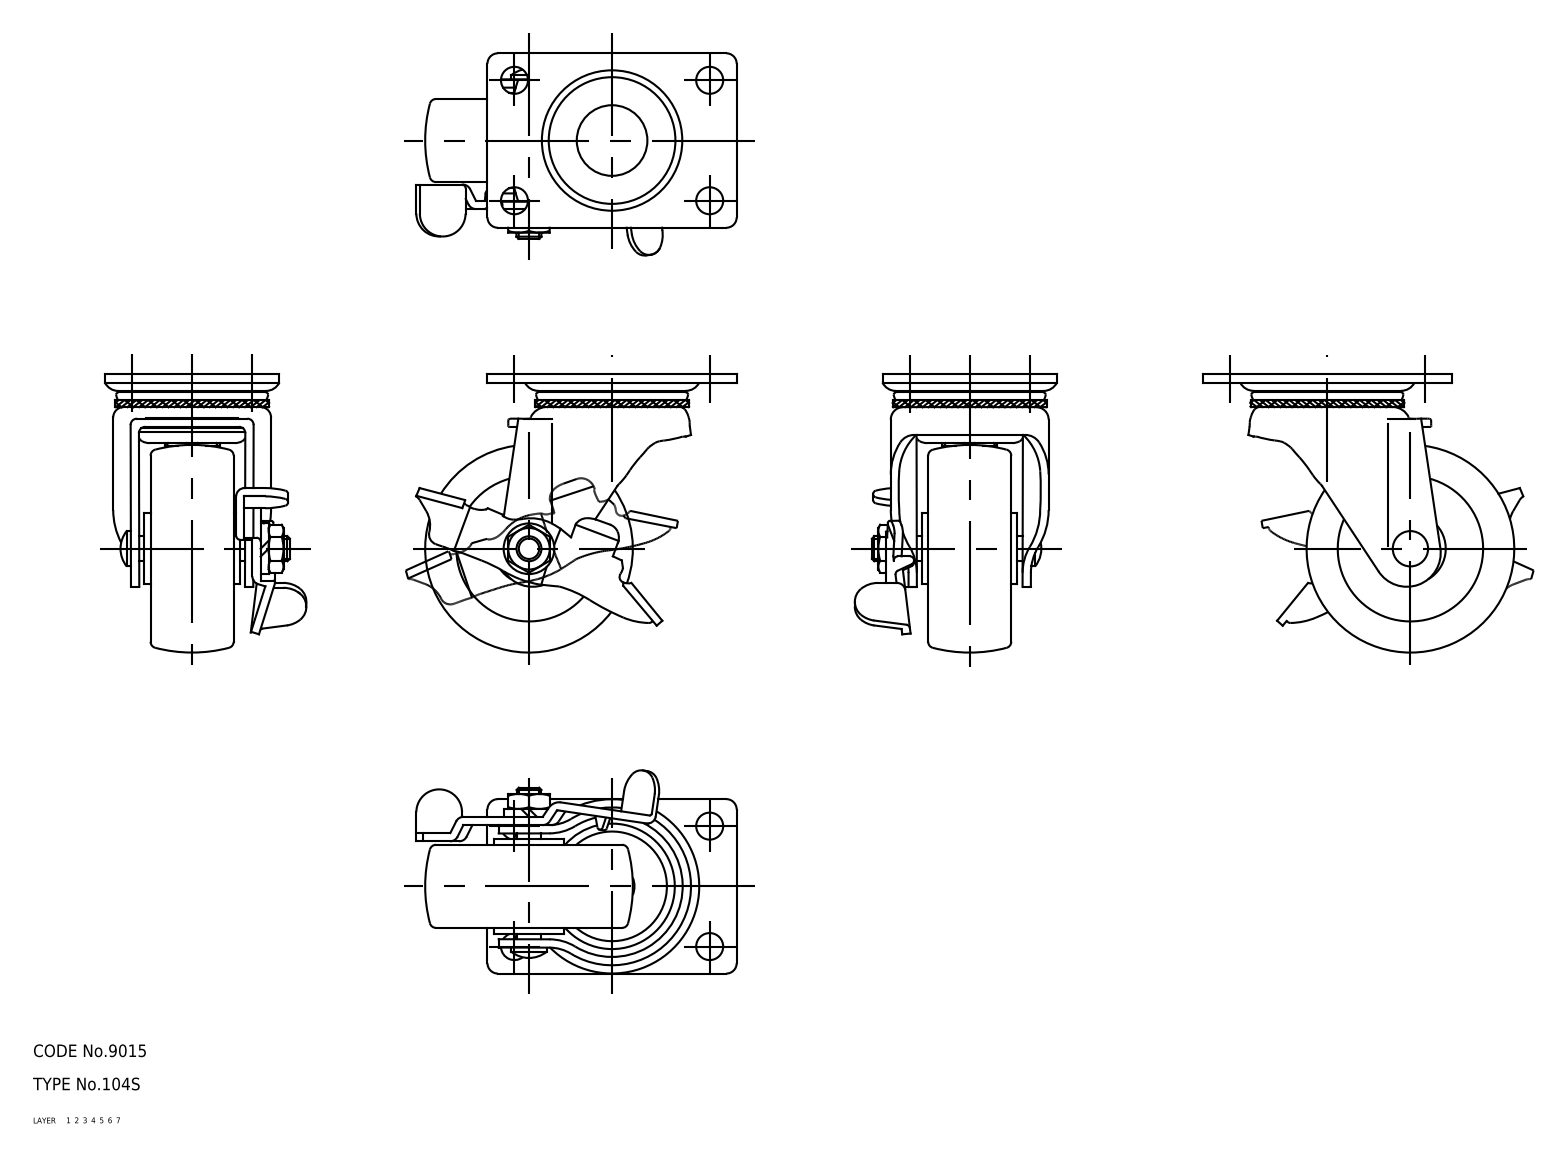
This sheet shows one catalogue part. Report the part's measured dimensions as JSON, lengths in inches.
{"part_name": "axle; wheel; mounting plate; main shaft (+2 more)", "step_written_by": "CADfix (AUTOMOTIVE_DESIGN)", "units": "inches", "bodies": {"solids": 6, "faces": 302, "planar": 0, "cylindrical": 0, "other": 302}, "overall_size": [3.039, 2.638, 1.921], "volume_in3": 3.785, "surface_area_in2": 41.3}
